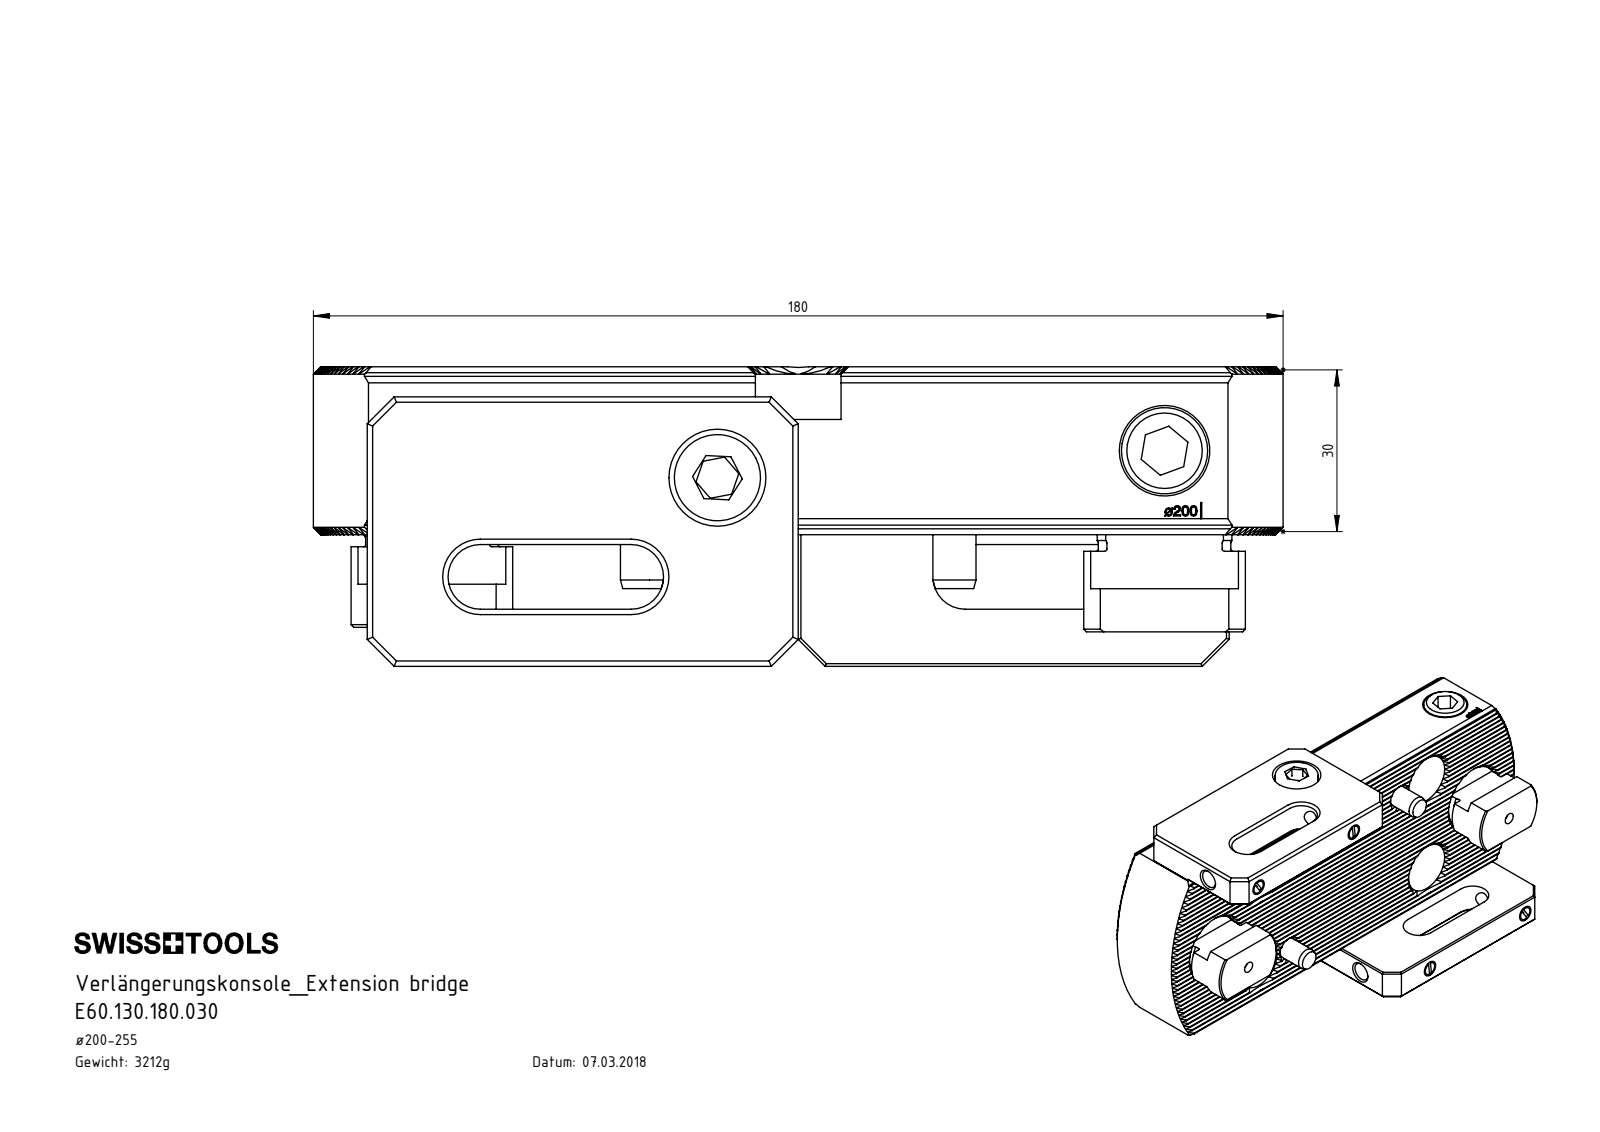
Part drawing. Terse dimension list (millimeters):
name: VK1-ER2.201.010_A_gespannt; VK1-ER2.101.010_A; VK1-ER2.001.044_A; E60.130.180.030 (+8 more)
written by: SolidWorks 2017 (CONFIG_CONTROL_DESIGN)
unit: mm
bodies: 25 solids, 1771 faces (971 planar, 477 cylindrical, 323 other)
size: 180 × 95 × 55.58
volume: 418 741 mm³; area: 114 296 mm²
holes: 4× ⌀5, 4× ⌀6, 4× ⌀6.8, 4× ⌀13, 4× ⌀19, 2× ⌀2, 2× ⌀8, 2× ⌀8.5, 2× ⌀10.5, 2× ⌀11, 2× ⌀14, 2× ⌀18
bosses: 4× ⌀16, 4× ⌀6, 2× ⌀10
rounds: 66× R0.14, 8× R2, 4× R6, 2× R12.3, 2× R15, 2× R65, 1× R7.95
face distances: 12, 82, 70, 1.73, 0.5, 82.5, 11.5, 70.5, 94, 3.46
hole spacings: 31.24, 113.77, 136, 7.9, 15, 18.55, 19.61, 31.89
